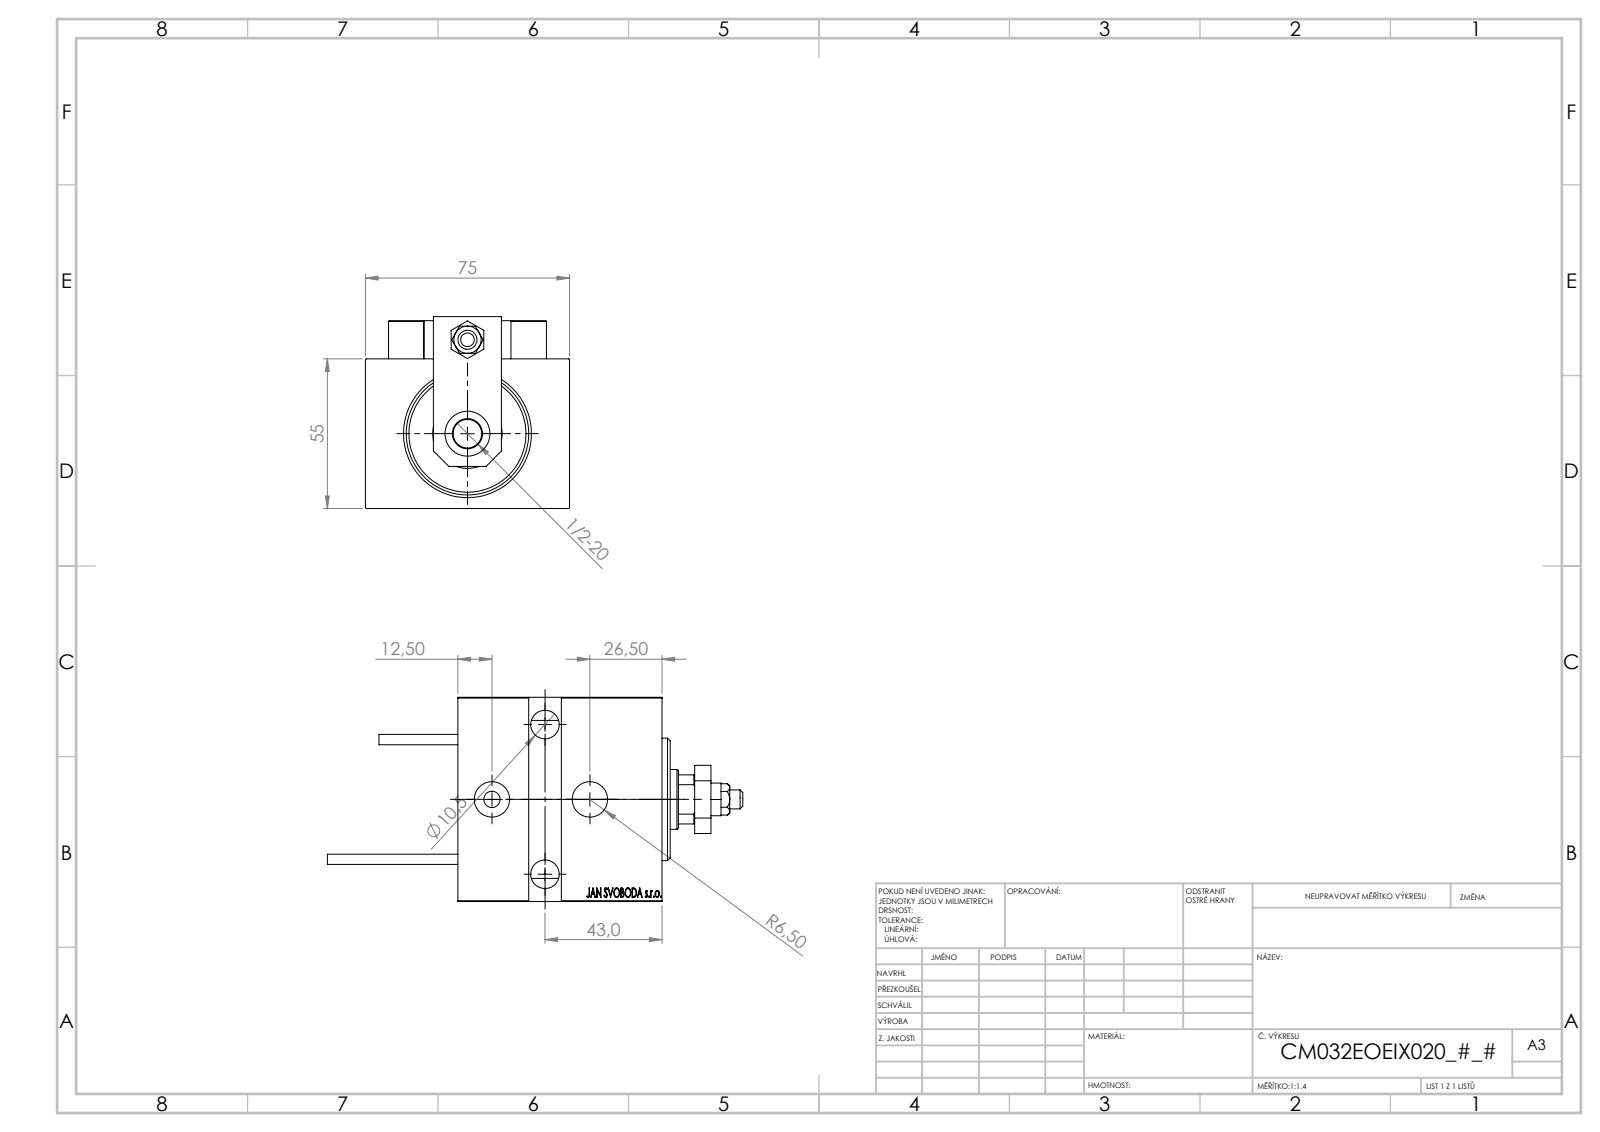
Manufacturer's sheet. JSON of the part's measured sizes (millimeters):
{"part_name": "SWITCH X; MAGNET; V450CM_E_Body; ALLEN BOLT D5 (+7 more)", "step_written_by": "SolidWorks 2019 (CONFIG_CONTROL_DESIGN)", "units": "millimeters", "bodies": {"solids": 24, "faces": 1273, "planar": 566, "cylindrical": 166, "other": 541}, "overall_size": [152.7, 75, 70.5], "volume_mm3": 337480, "surface_area_mm2": 76290, "round_holes": [[8, 5], [3.2, 4], [4, 4], [10.5, 3], [16.5, 3], [5, 2], [13, 2], [7, 1], [22, 1], [25.5, 1], [32, 1], [45, 1]], "round_bosses_or_shafts": [[5, 2], [3.8, 2], [34, 1], [13, 1], [11, 1], [6, 1]], "partial_cylinders_radius": [[0.3, 30], [3, 2], [10.5, 1]], "face_to_face_distances": [75, 55, 3, 10, 12, 14, 65, 25, 7, 5], "hole_center_spacings": [11.37, 12.5, 20, 21.91, 27.07, 29.59, 29.69, 32.07]}
